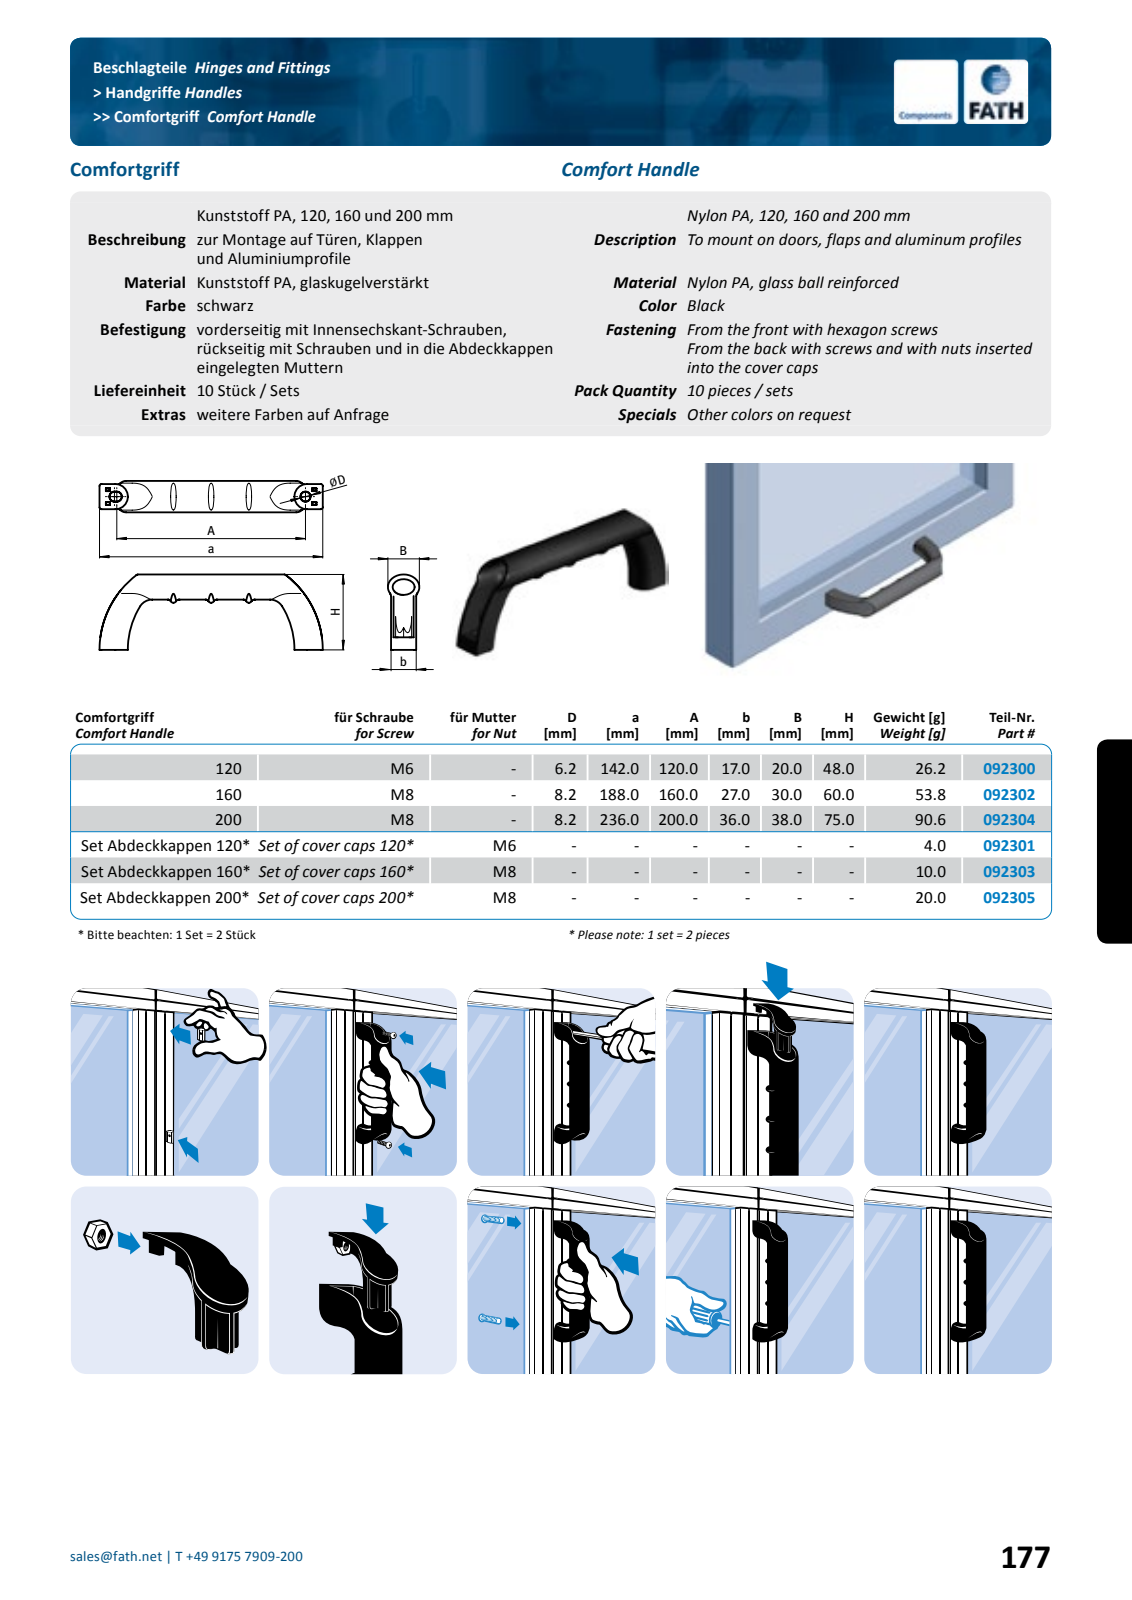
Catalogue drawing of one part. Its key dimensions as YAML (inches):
part_name: "fath_092304"
step_written_by: "Spatial InterOp 3D (automotive_design)"
units: inches
bodies: {solids: 1, faces: 346, planar: 70, cylindrical: 60, other: 216}
overall_size: [9.291, 2.953, 1.496]
volume: 4.918
surface_area: 87.98
round_holes:
  - {diameter: 0.315, count: 1}
partial_cylinders:
  - {radius: 0.039, count: 20}
  - {radius: 0.059, count: 8}
  - {radius: 0.118, count: 2}
  - {radius: 3.383, count: 2}
  - {radius: 3.15, count: 1}
face_to_face_distances: [1.417, 1.05, 0.315, 0.197, 0.118, 1.118, 0.647, 0.451, 8.858, 8.489]
